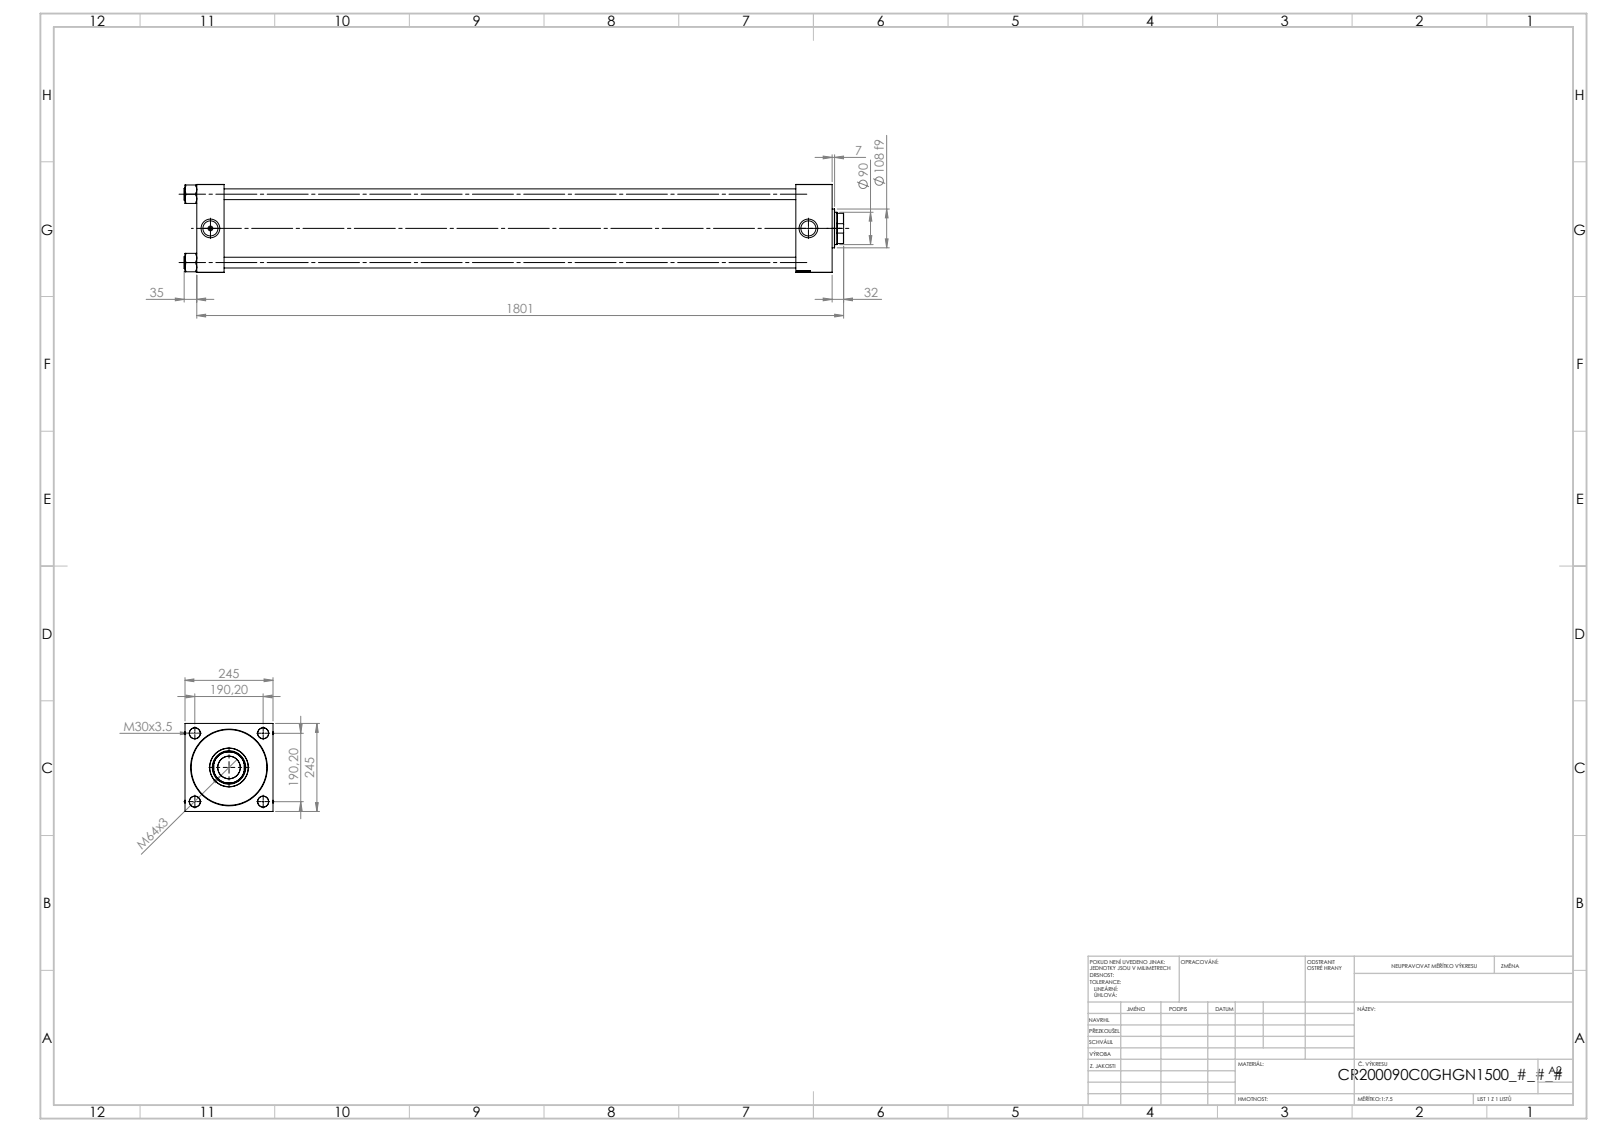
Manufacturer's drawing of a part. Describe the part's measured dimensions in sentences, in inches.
The part is named "V215CR_C_TYCINKA; V215_VC_A; V215CR_C_Body; V215CR_VCP_C (+1 more)". Its 3-D file was written by "SolidWorks 2019 (CONFIG_CONTROL_DESIGN)". It is 11 solids with 1196 faces: 574 planar, 86 cylindrical and 536 other. Overall it measures 72.283 by 9.82 by 9.646 inches. Its volume is 1 823 cubic inches and its surface area 6 050 square inches. Round holes: 4 of diameter 1.181, 2 of diameter 0.276, 2 of diameter 1.65, 2 of diameter 2.047, 1 of diameter 2.461, 1 of diameter 3.543, 1 of diameter 3.661, 1 of diameter 5.748, 1 of diameter 7.874, 1 of diameter 8.287. Round bosses or shafts: 4 of diameter 1.299, 1 of diameter 8.11, 1 of diameter 4.252. Partial cylindrical surfaces (rounded edges, fillets, slot ends): 1 of radius 1.732. The main face-to-face distances are 9.646, 2.992, 69.646, 66.654, 68.516, 65.524, 1.13, 65.669, 62.677, 2.846. The hole center spacings are 5.295, 7.488, 10.59, 65.551.
